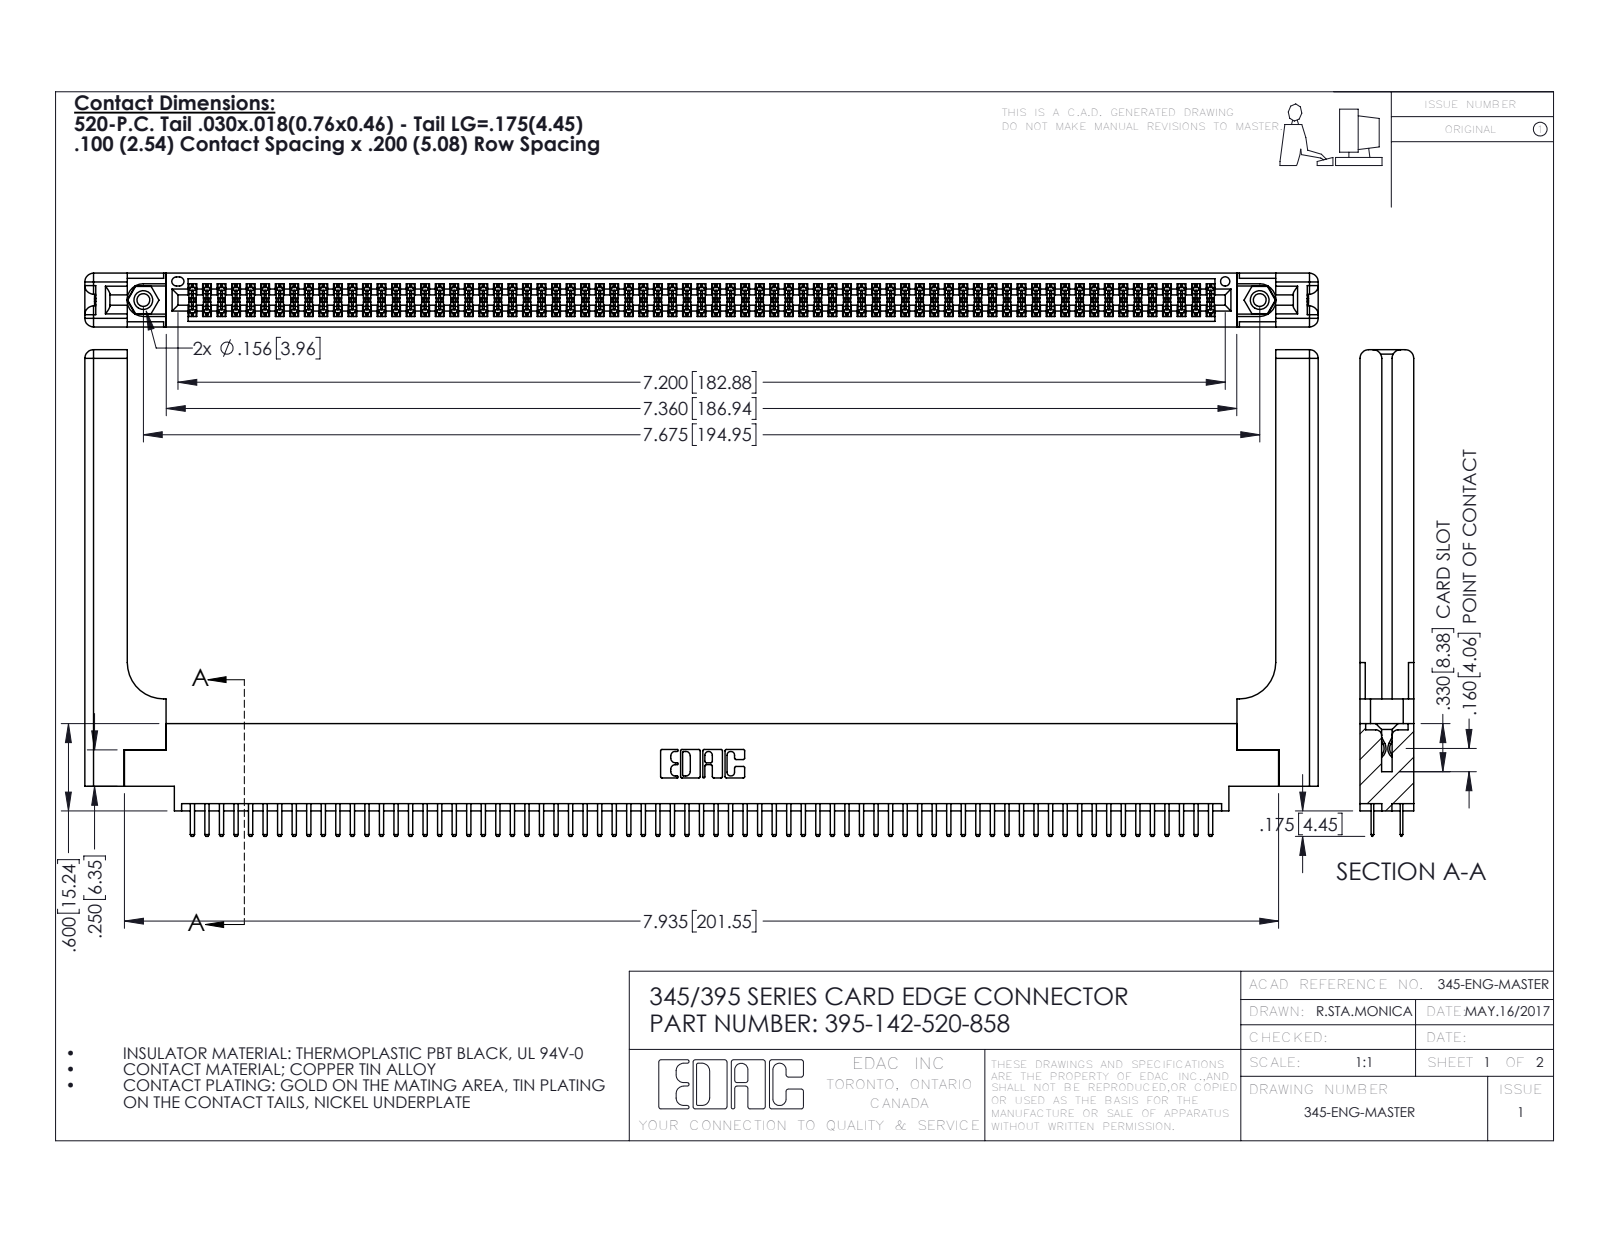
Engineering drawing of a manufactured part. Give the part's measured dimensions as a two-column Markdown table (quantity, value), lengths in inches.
| quantity | value |
| --- | --- |
| part name | 345 Part_0.170 Offset - 0.156 Dia-TH; 345-220-058_345-220-058; 345-250-001_345-250-001-102; 395-142-520-858 (+1 more) |
| STEP written by | SolidWorks 2016 (CONFIG_CONTROL_DESIGN) |
| units | inches |
| bodies | 147 solids, 8054 faces (5202 planar, 2792 cylindrical, 60 other) |
| overall size | 8.479 × 3.345 × 0.37 |
| volume | 1.8 in³ |
| surface area | 56.88 in² |
| round holes (diameter × count) | 0.089 × 2, 0.125 × 2, 0.156 × 2, 0.064 × 1 |
| round bosses / shafts (diameter × count) | 0.155 × 2 |
| partial cylindrical surfaces (radius × count) | 0.006 × 213, 0.01 × 146, 0.01 × 22, 0.06 × 16, 0.007 × 6, 0.031 × 6, 0.026 × 3, 0.014 × 2 |
| main face-to-face distances | 0.072, 0.298, 0.37, 0.2, 0.098, 0.272, 0.025, 0.225, 0.022, 0.175 |
| hole center spacings | 0.27, 7.439, 7.675 |
